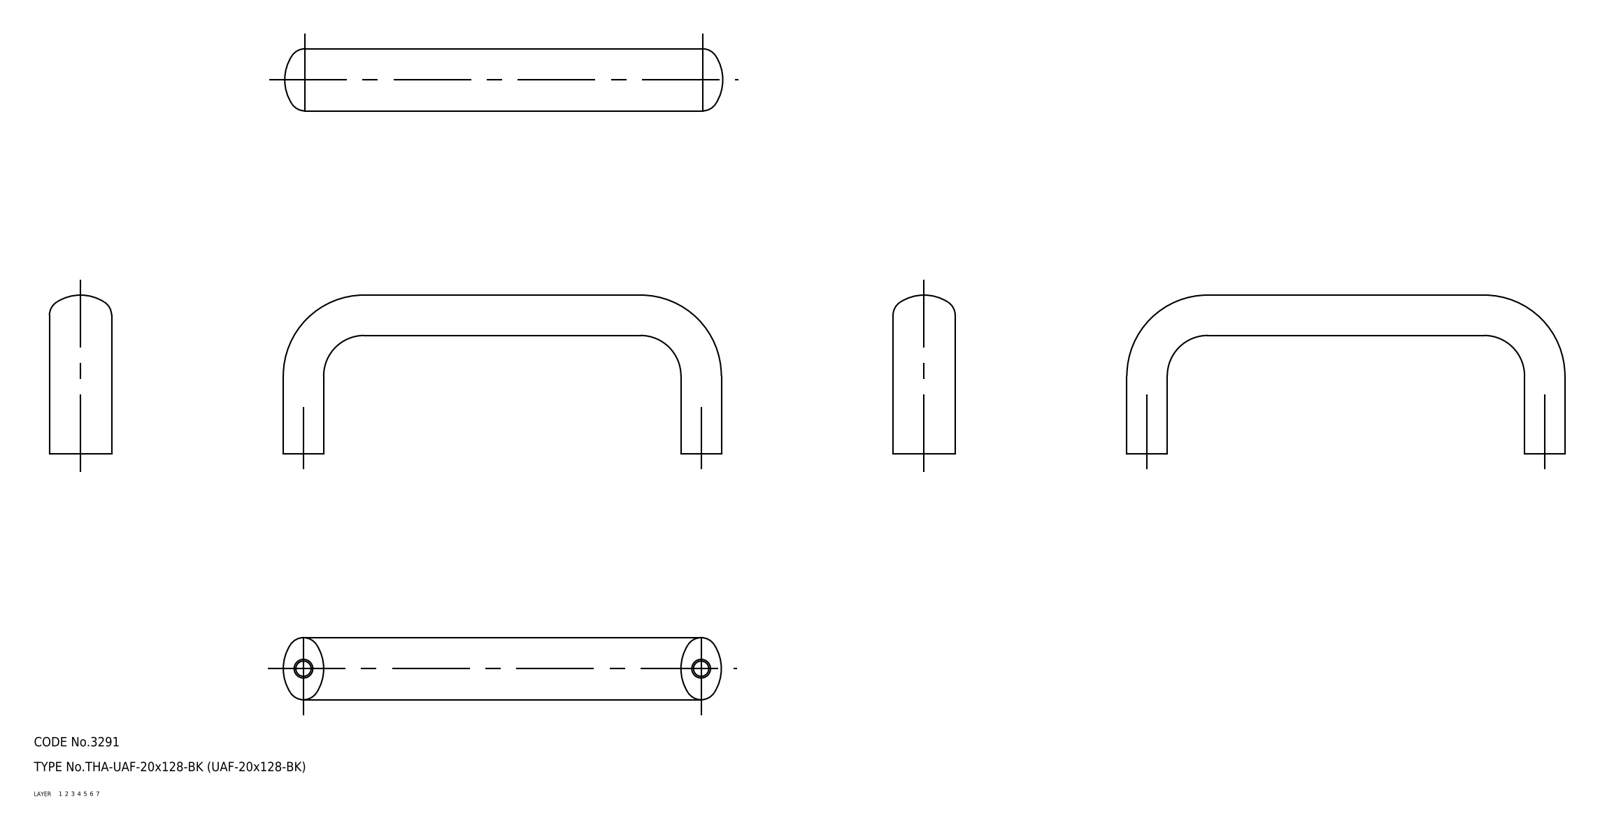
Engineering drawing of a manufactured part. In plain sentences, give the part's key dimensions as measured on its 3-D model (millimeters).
The part is named "pull". Its 3-D file was written by "CADfix (AUTOMOTIVE_DESIGN)". It is 1 solid with 18 faces: 0 planar, 0 cylindrical and 18 other. Overall it measures 141 by 51.01 by 20 millimeters. Its volume is 40 276 cubic millimeters and its surface area 11 278 square millimeters.
